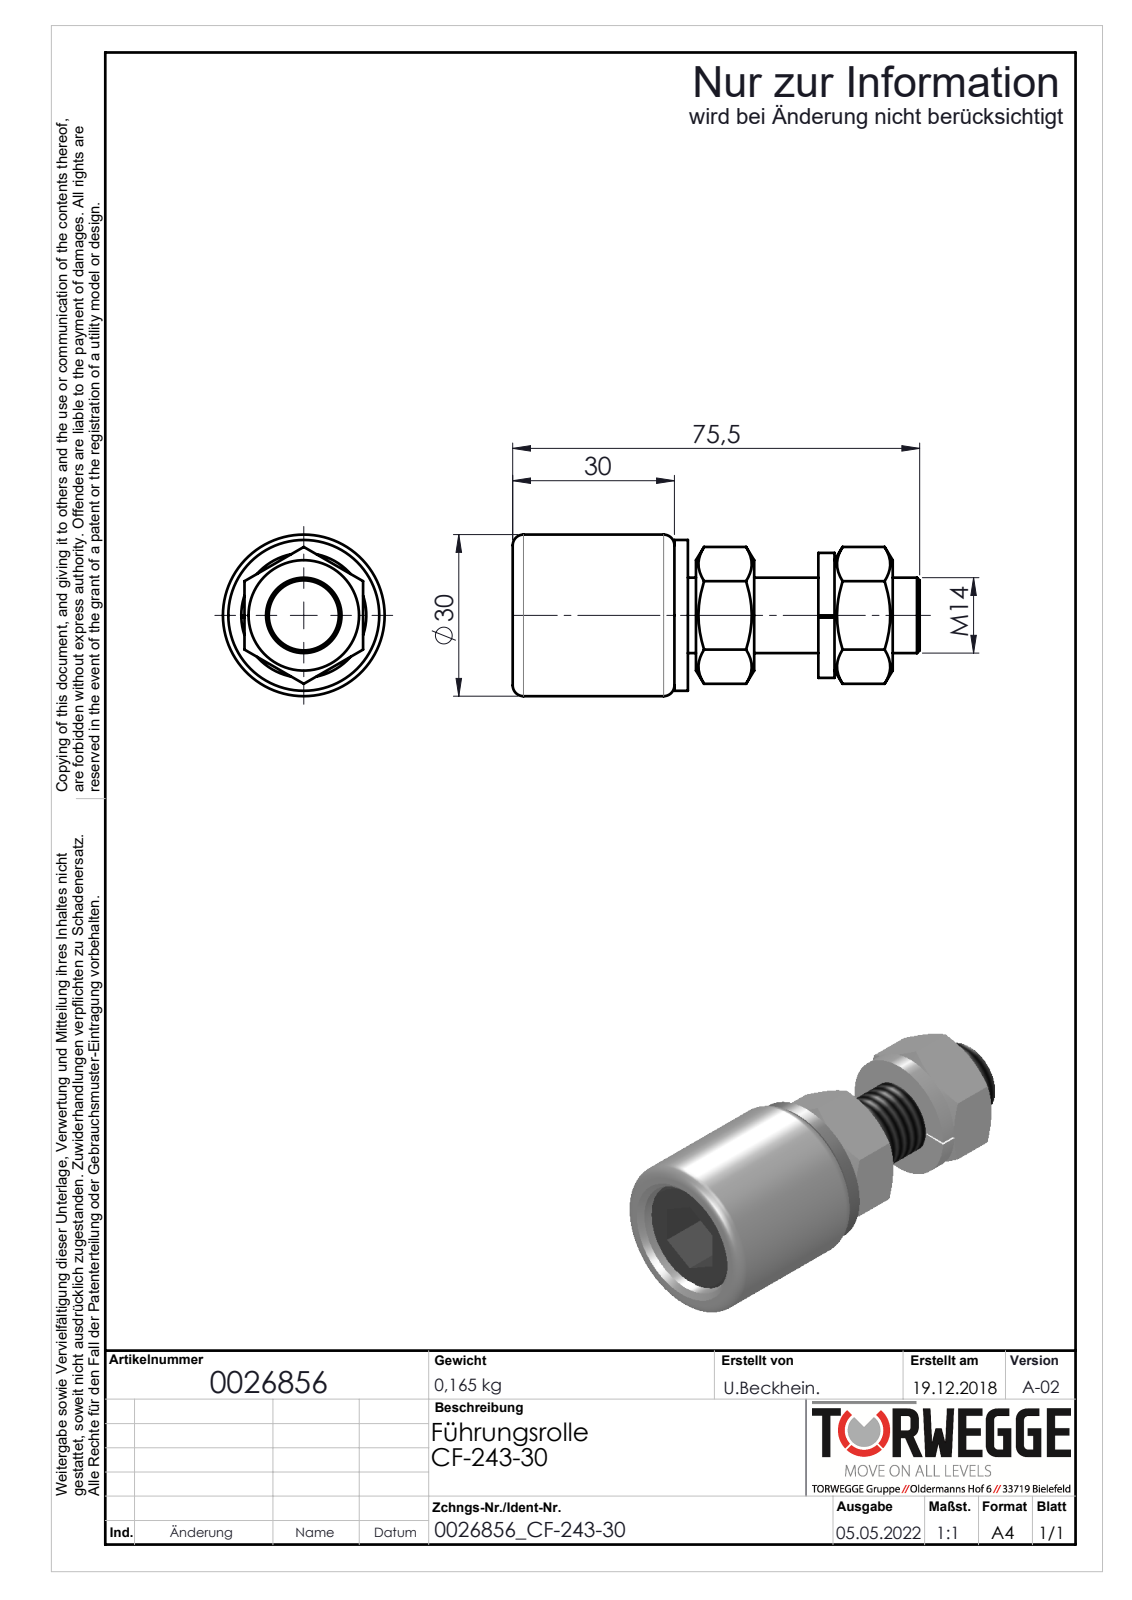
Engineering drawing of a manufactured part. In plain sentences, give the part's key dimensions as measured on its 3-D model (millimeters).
The part is named "0026856". Its 3-D file was written by "SolidWorks 2020 (AUTOMOTIVE_DESIGN)". It is 6 solids with 89 faces: 35 planar, 24 cylindrical and 30 other. Overall it measures 75.5 by 30 by 30 millimeters. Its volume is 33 533 cubic millimeters and its surface area 15 543 square millimeters. Round holes: 1 of diameter 12, 1 of diameter 14.2, 1 of diameter 15, 1 of diameter 21.8. Round bosses or shafts: 1 of diameter 30, 1 of diameter 28, 1 of diameter 23.2, 1 of diameter 21, 1 of diameter 14. The main face-to-face distances are 22, 5, 14, 2.5, 29.7, 27.2, 17, 10.8, 25.7, 16.5.
